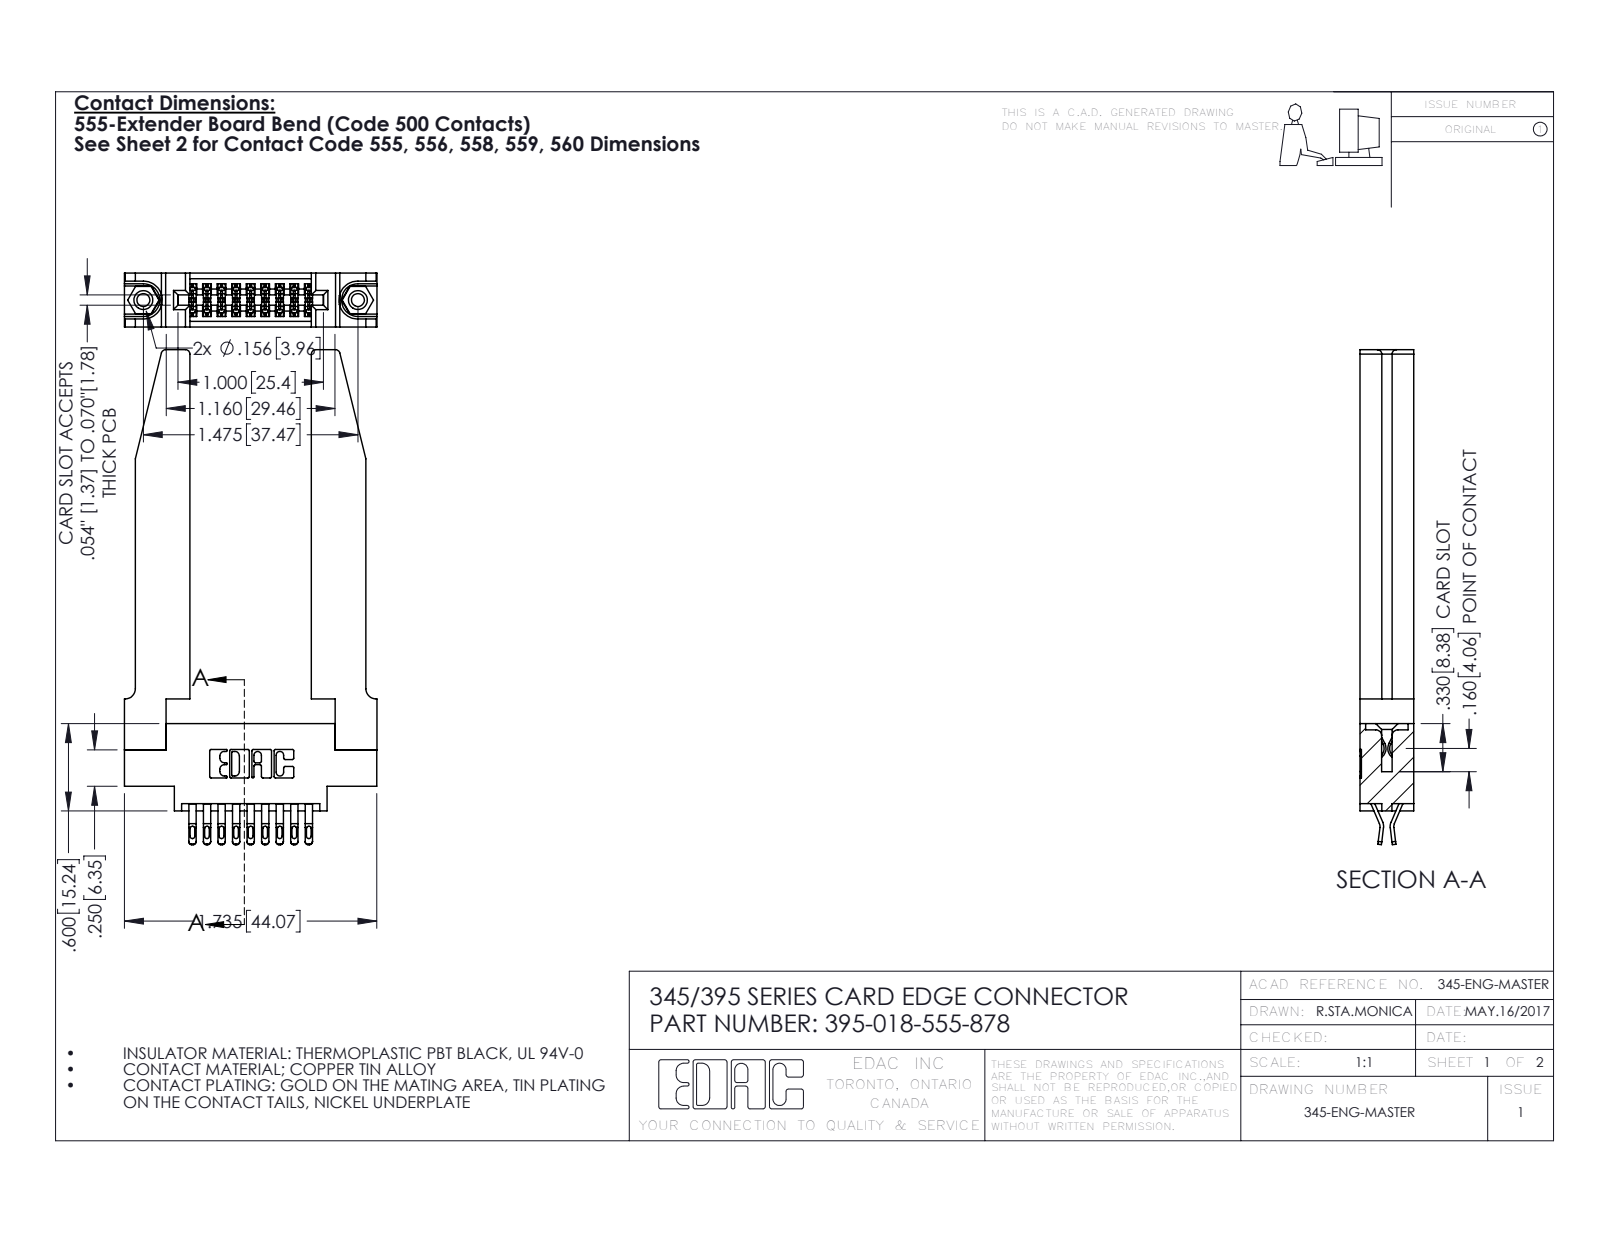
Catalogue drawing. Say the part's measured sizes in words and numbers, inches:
The part is named "345-220-078_345-220-078; 345-292-001_555 Tail; 395-018-555-878; 345 Part_0.170 Offset - 0.156 Dia-TH (+1 more)". Its 3-D file was written by "SolidWorks 2016 (CONFIG_CONTROL_DESIGN)". It is 23 solids with 1372 faces: 784 planar, 536 cylindrical and 52 other. Overall it measures 3.402 by 1.736 by 0.37 inches. Its volume is 0.713 cubic inches and its surface area 19.08 square inches. Round holes: 2 of diameter 0.089, 2 of diameter 0.125, 2 of diameter 0.156, 1 of diameter 0.064. Round bosses or shafts: 2 of diameter 0.155. Partial cylindrical surfaces (rounded edges, fillets, slot ends): 45 of radius 0.016, 36 of radius 0.02, 27 of radius 0.006, 22 of radius 0.01, 8 of radius 0.03, 6 of radius 0.007, 6 of radius 0.031, 3 of radius 0.026. The main face-to-face distances are 0.37, 0.072, 0.298, 0.148, 0.15, 0.22, 0.077, 0.835, 0.025, 0.095. The hole center spacings are 0.27, 1.244, 1.475.
